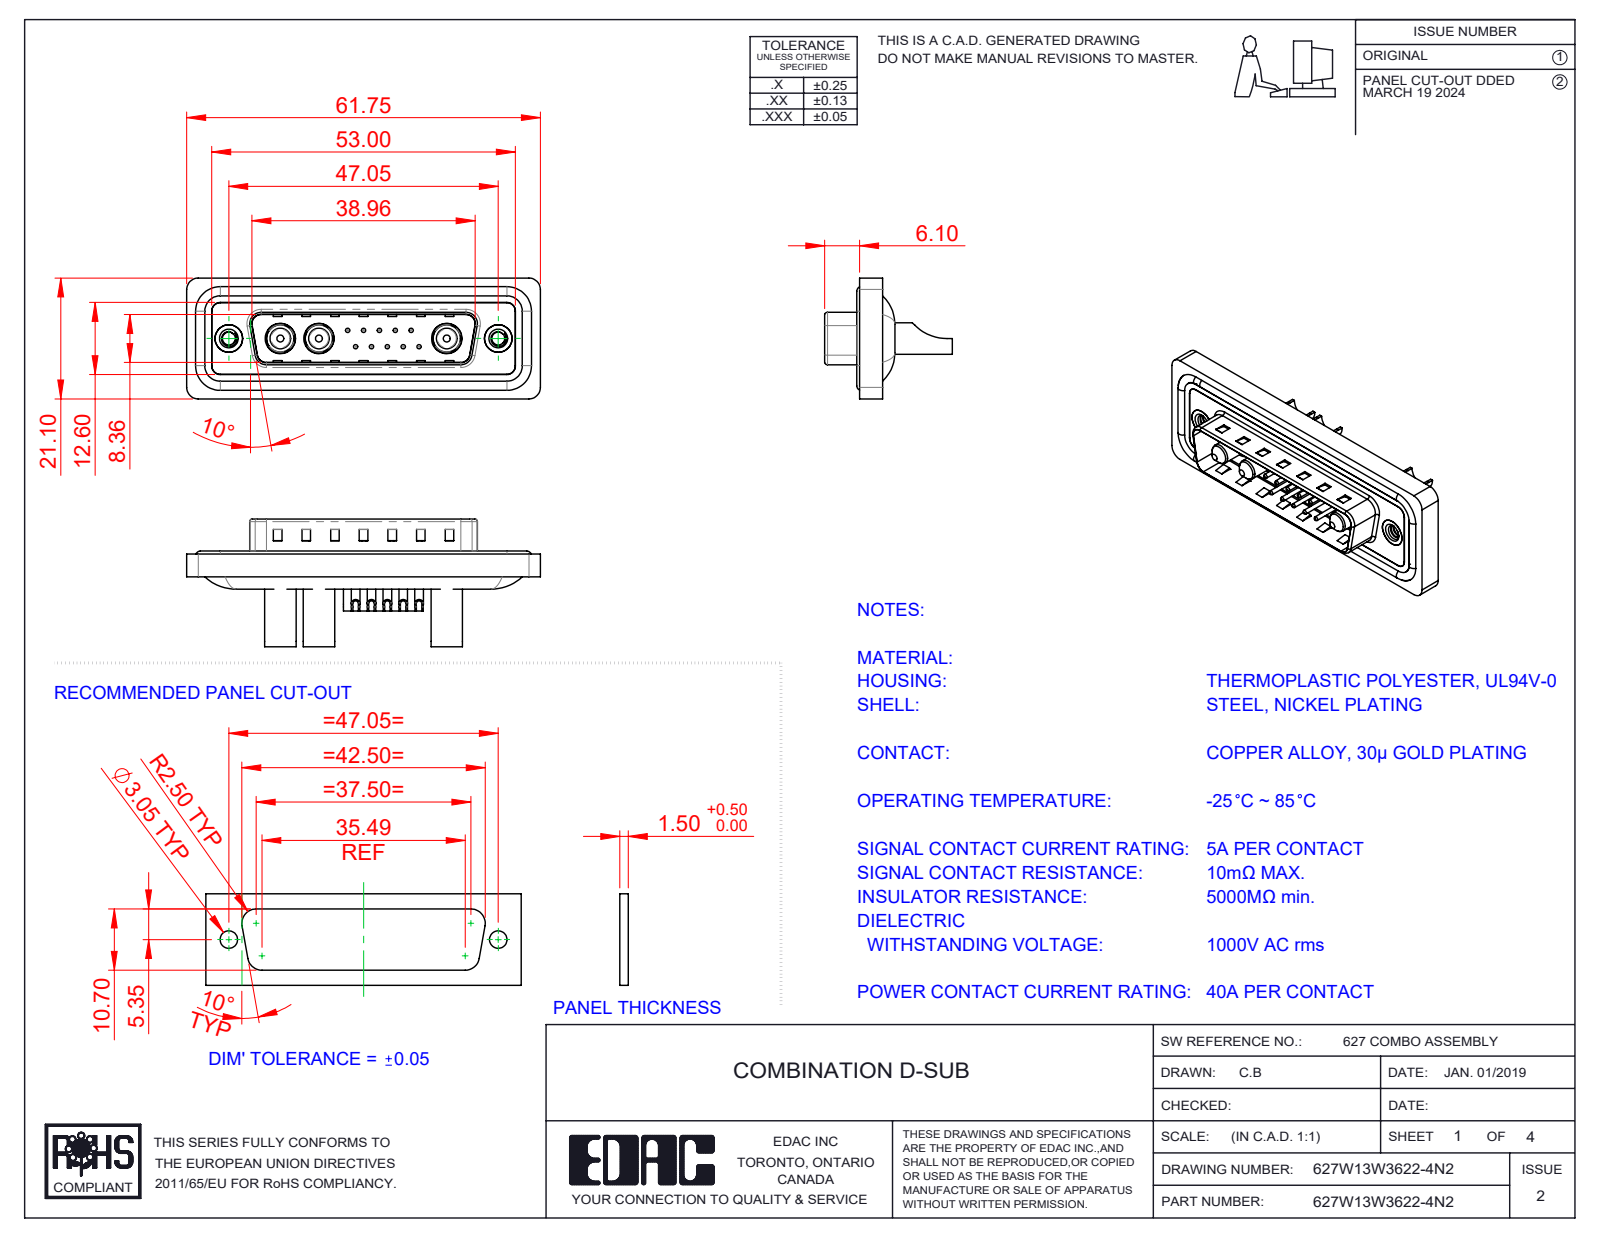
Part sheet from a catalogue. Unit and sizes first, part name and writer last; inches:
Units: inches
Overall size (bounding box): 2.431 × 0.878 × 0.831
Round holes (diameter × count): ⌀0.03 ×10, ⌀0.039 ×10, ⌀0.063 ×10, ⌀0.079 ×10, ⌀0.181 ×3, ⌀0.191 ×3, ⌀0.209 ×3, ⌀0.089 ×2, ⌀0.157 ×2, ⌀0.189 ×2, ⌀0.197 ×2
Round bosses / shafts (diameter × count): ⌀0.059 ×10, ⌀0.063 ×4, ⌀0.217 ×3, ⌀0.205 ×3, ⌀0.187 ×3, ⌀0.148 ×3, ⌀0.142 ×3, ⌀0.193 ×2
Partial cylindrical surfaces — rounded edges, fillets, slot ends (radius × count): R0.059 ×22, R0.079 ×18, R0.02 ×8, R0.063 ×8, R0.039 ×6, R0.01 ×4, R0.024 ×4, R0.026 ×4
Main face-to-face distances: 0.016, 0.043, 0.059, 0.063, 0.02, 0.122, 0.114, 0.032, 0.377, 0.161
Hole centre spacings: 0.124, 0.109, 0.198, 0.218, 0.295, 0.198, 0.327, 0.398
Volume: 0.456 in³ · Surface area: 19.18 in²
Bodies: 23 solids, 982 faces (335 planar, 408 cylindrical, 239 other)
Part name (STEP PRODUCT): 627Combo Shell Rear_25 Contacts; 627Combo Shell Front_25 Contacts; Power Pin_40A SC; 627Combo Contact Row 1_22 (+5 more)
STEP written by: SolidWorks 2023 (CONFIG_CONTROL_DESIGN)
